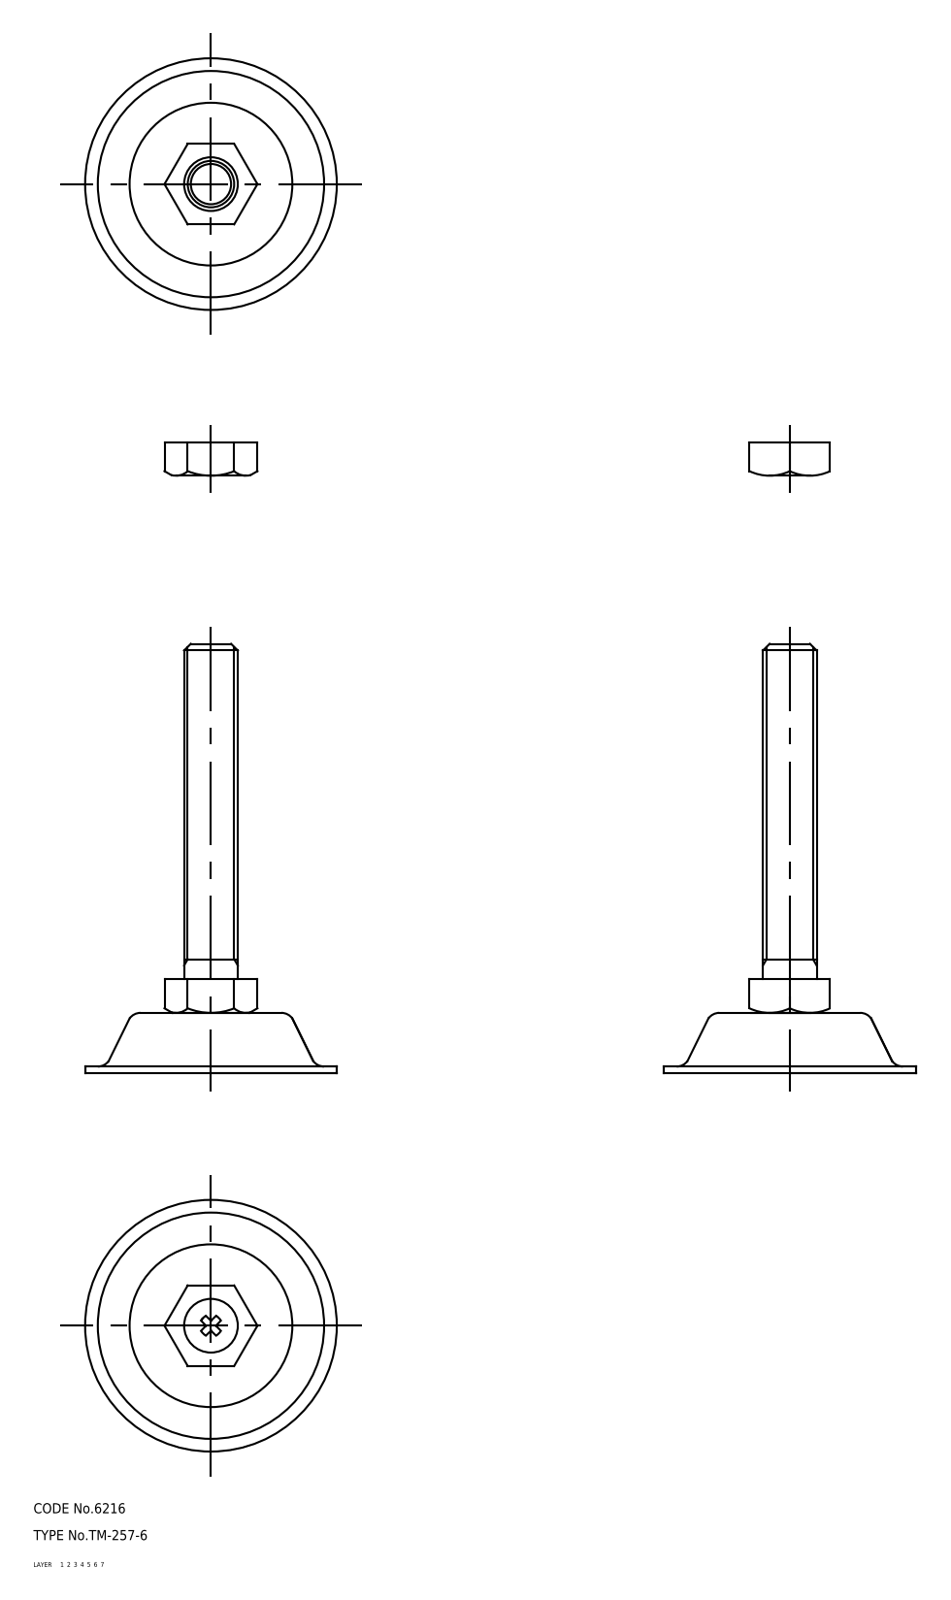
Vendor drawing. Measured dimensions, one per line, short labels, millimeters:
name: nut; foot; bolt; TM_257_6_9913_36
written by: CADfix (AUTOMOTIVE_DESIGN)
unit: mm
bodies: 4 solids, 83 faces (0 planar, 0 cylindrical, 83 other)
size: 128 × 75 × 75
volume: 44 956 mm³; area: 23 306 mm²
